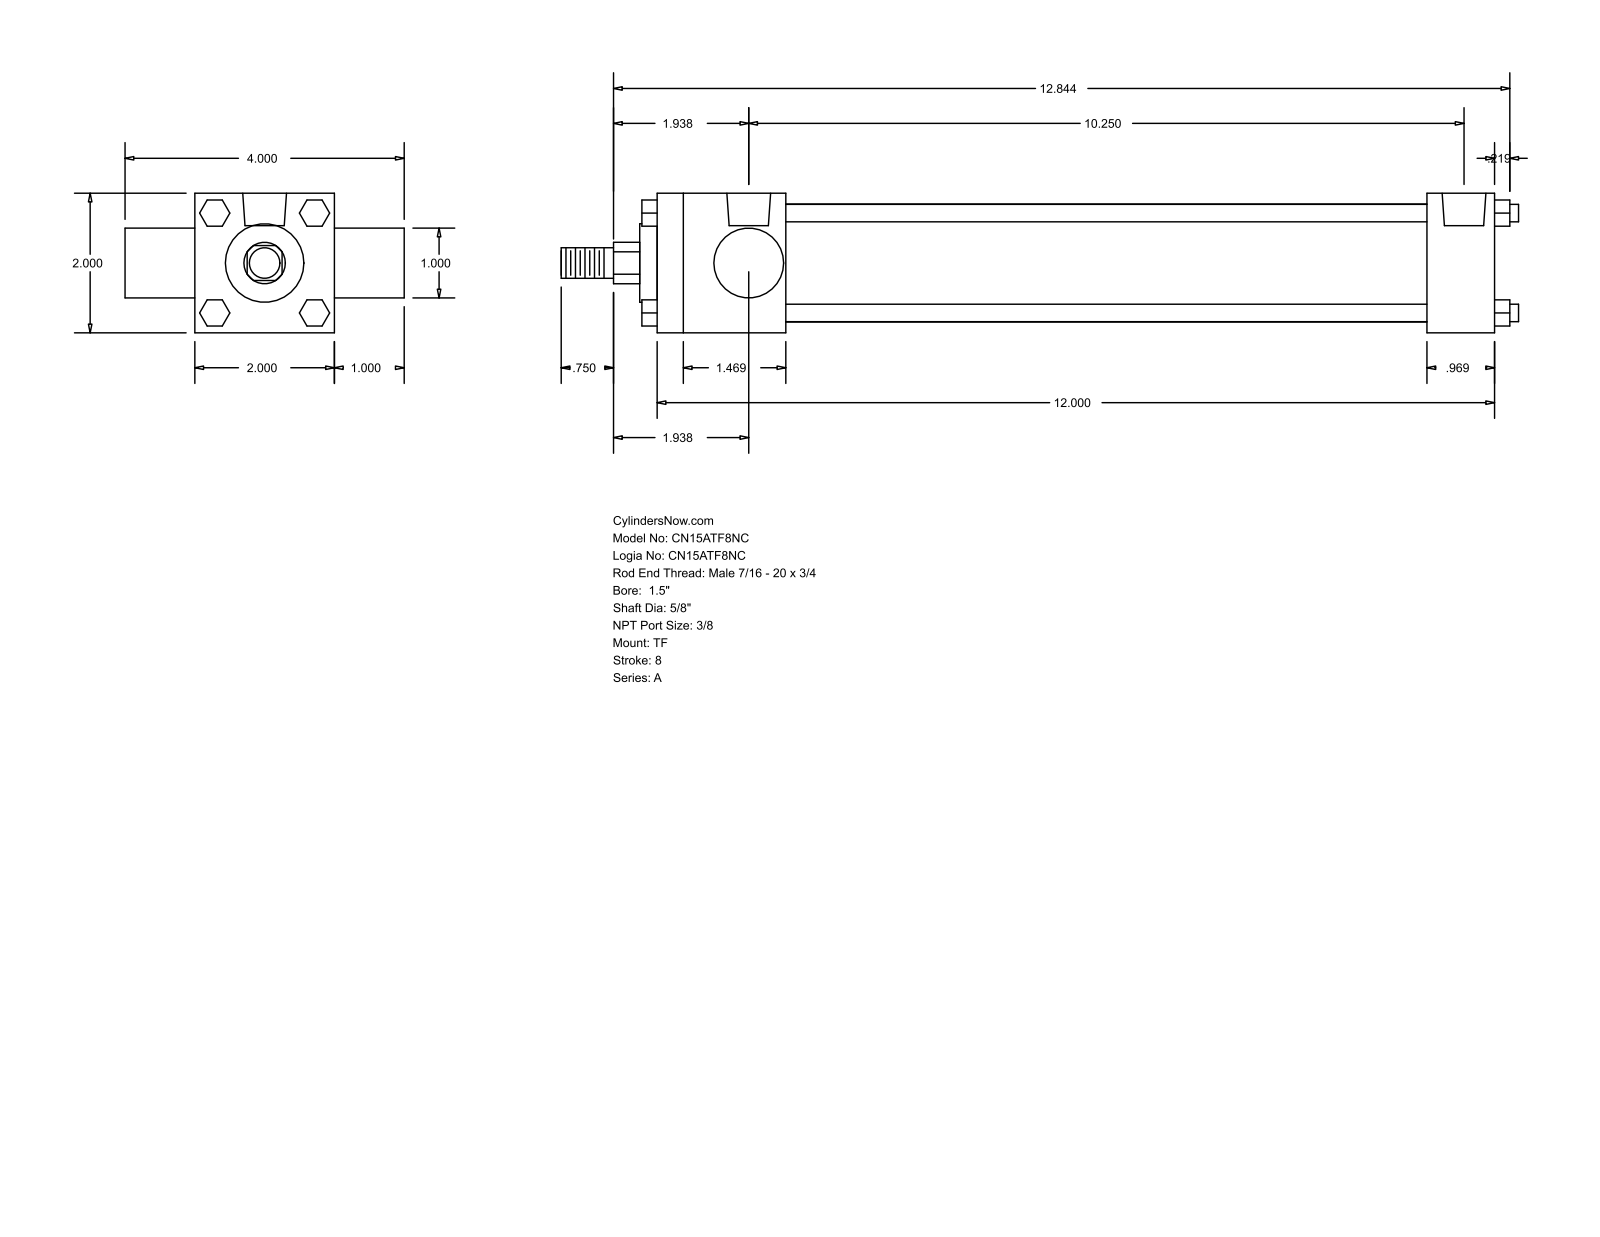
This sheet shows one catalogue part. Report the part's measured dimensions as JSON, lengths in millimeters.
{"part_name": "A_TF__0150_0.625", "step_written_by": "GSSL Pune (CONFIG_CONTROL_DESIGN)", "units": "millimeters", "bodies": {"solids": 0, "faces": 120, "planar": 92, "cylindrical": 28, "other": 0}, "overall_size": [348.46, 101.6, 50.8], "round_holes": [[5.56, 3], [15.93, 2]], "round_bosses_or_shafts": [[6.35, 4], [42.93, 1], [28.57, 1], [25.4, 1], [15.88, 1], [11.11, 1]], "partial_cylinders_radius": [[7.54, 1]], "face_to_face_distances": [50.8, 304.8, 25.4, 76.2, 46.83, 280.19, 233.36, 257.97, 24.61, 101.6], "hole_center_spacings": [3.97, 256.38, 252.41, 260.35]}
